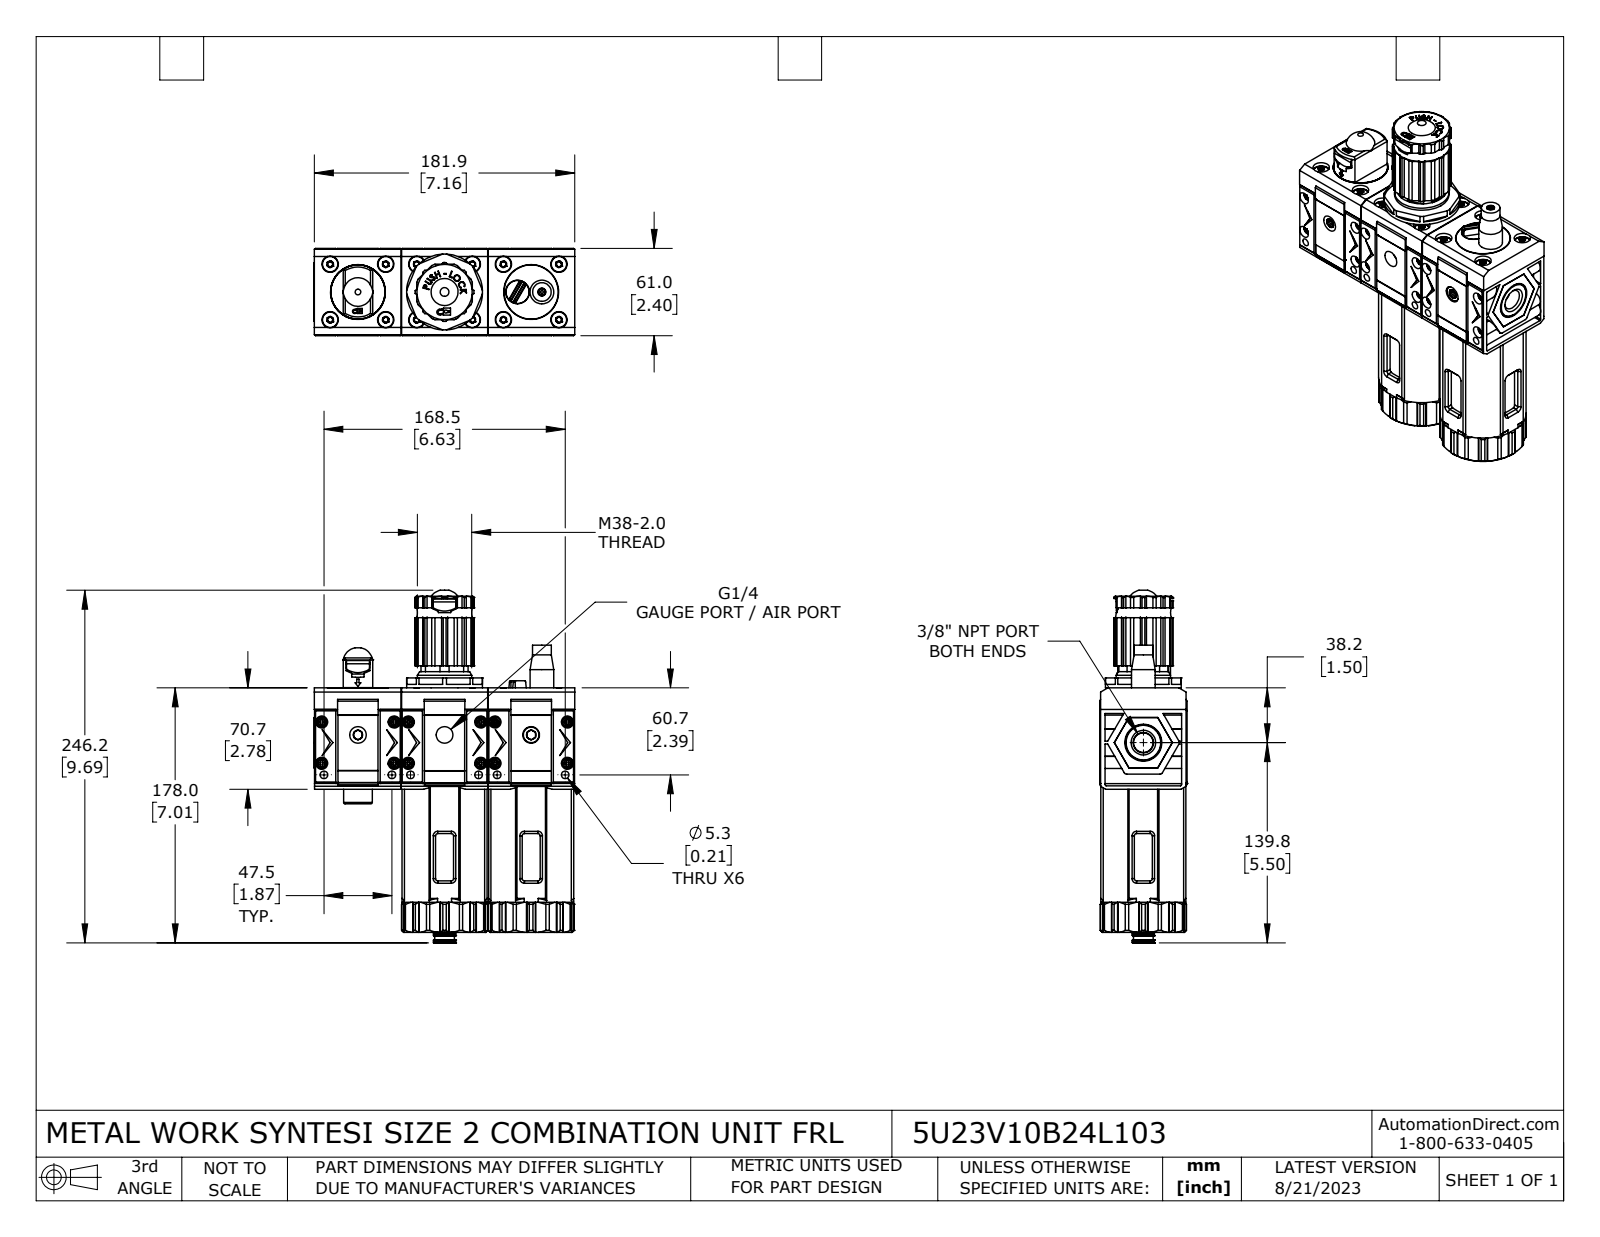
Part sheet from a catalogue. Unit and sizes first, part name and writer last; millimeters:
Units: millimetres
Overall size (bounding box): 246.2 × 182.2 × 61
Round holes (diameter × count): ⌀3.3 ×12, ⌀4.2 ×12, ⌀8.4 ×12, ⌀11.4 ×12, ⌀5.3 ×6, ⌀11.6 ×3, ⌀38.3 ×3, ⌀49 ×2, ⌀50 ×2, ⌀51 ×2, ⌀51.5 ×2, ⌀3.2 ×1
Round bosses / shafts (diameter × count): ⌀7 ×12, ⌀4.8 ×12, ⌀3.8 ×12, ⌀38 ×2, ⌀53 ×1, ⌀37.8 ×1, ⌀31.7 ×1, ⌀26.3 ×1
Partial cylindrical surfaces — rounded edges, fillets, slot ends (radius × count): R0.3 ×84, R0.5 ×32, R1.5 ×16, R1.8 ×12, R4.9 ×12, R6.1 ×6, R20.5 ×4, R3 ×3
Main face-to-face distances: 60.5, 60.7, 2.4, 55.7, 53.3, 61, 60.3, 79, 134.7, 81.4
Hole centre spacings: 60.5, 27.4, 38.8, 121, 45.4, 67, 71.9, 82.2
Volume: 1 121 000 mm³ · Surface area: 325 200 mm²
Bodies: 40 solids, 3750 faces (2199 planar, 1017 cylindrical, 534 other)
Part name (STEP PRODUCT): 5U23V10B24L103
STEP written by: SolidWorks 2021 (CONFIG_CONTROL_DESIGN)
